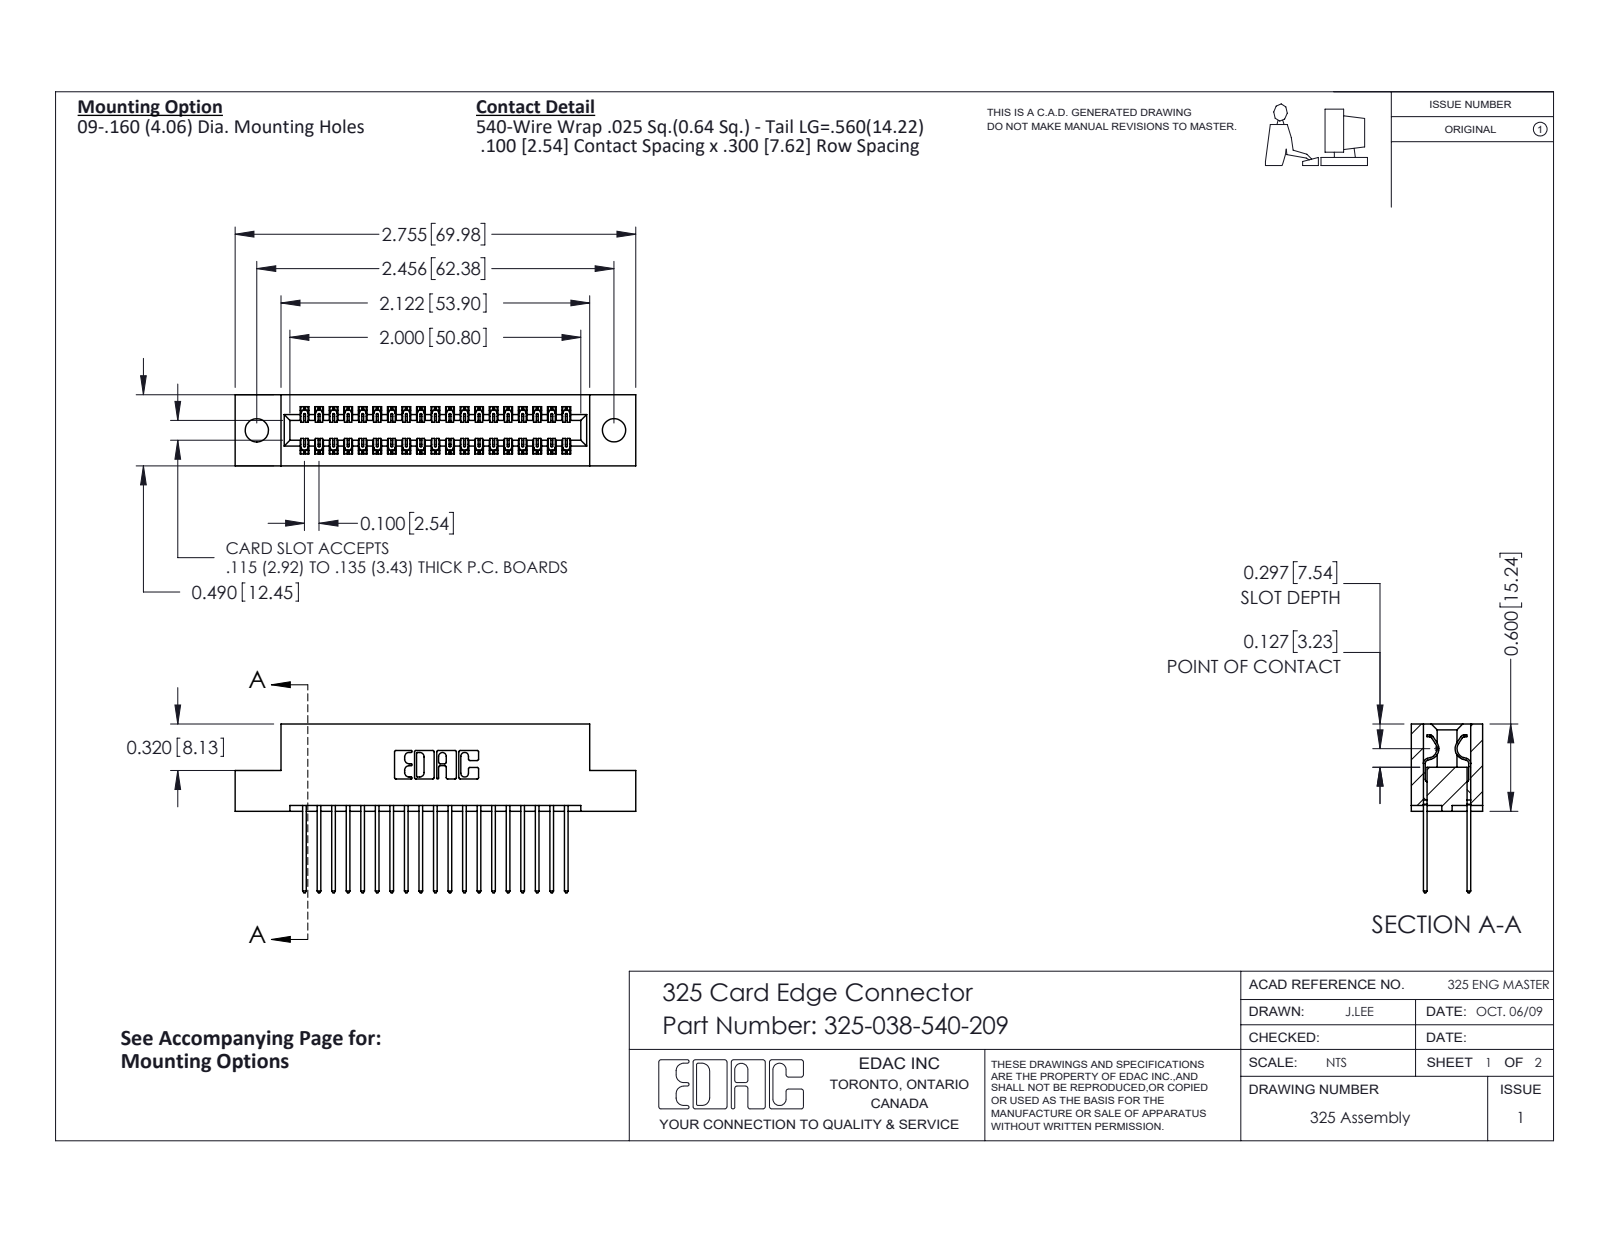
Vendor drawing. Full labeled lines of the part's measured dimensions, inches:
Part name (STEP PRODUCT): 325-038-540-209; 325-292-001_325-293-140; 325 Part_.160 TH
STEP written by: SolidWorks 2016 (CONFIG_CONTROL_DESIGN)
Units: inches
Bodies: 39 solids, 2090 faces (1438 planar, 652 cylindrical, 0 other)
Overall size (bounding box): 2.755 × 1.16 × 0.49
Volume: 0.533 in³ · Surface area: 16.49 in²
Round holes (diameter × count): ⌀0.16 ×2
Partial cylindrical surfaces — rounded edges, fillets, slot ends (radius × count): R0.006 ×57, R0.01 ×38, R0.01 ×22, R0.007 ×6, R0.031 ×6, R0.026 ×3, R0.014 ×2, R0.022 ×2
Main face-to-face distances: 0.083, 0.407, 0.3, 0.107, 0.383, 0.025, 0.49, 0.325, 0.04, 0.275
Hole centre spacings: 2.456
